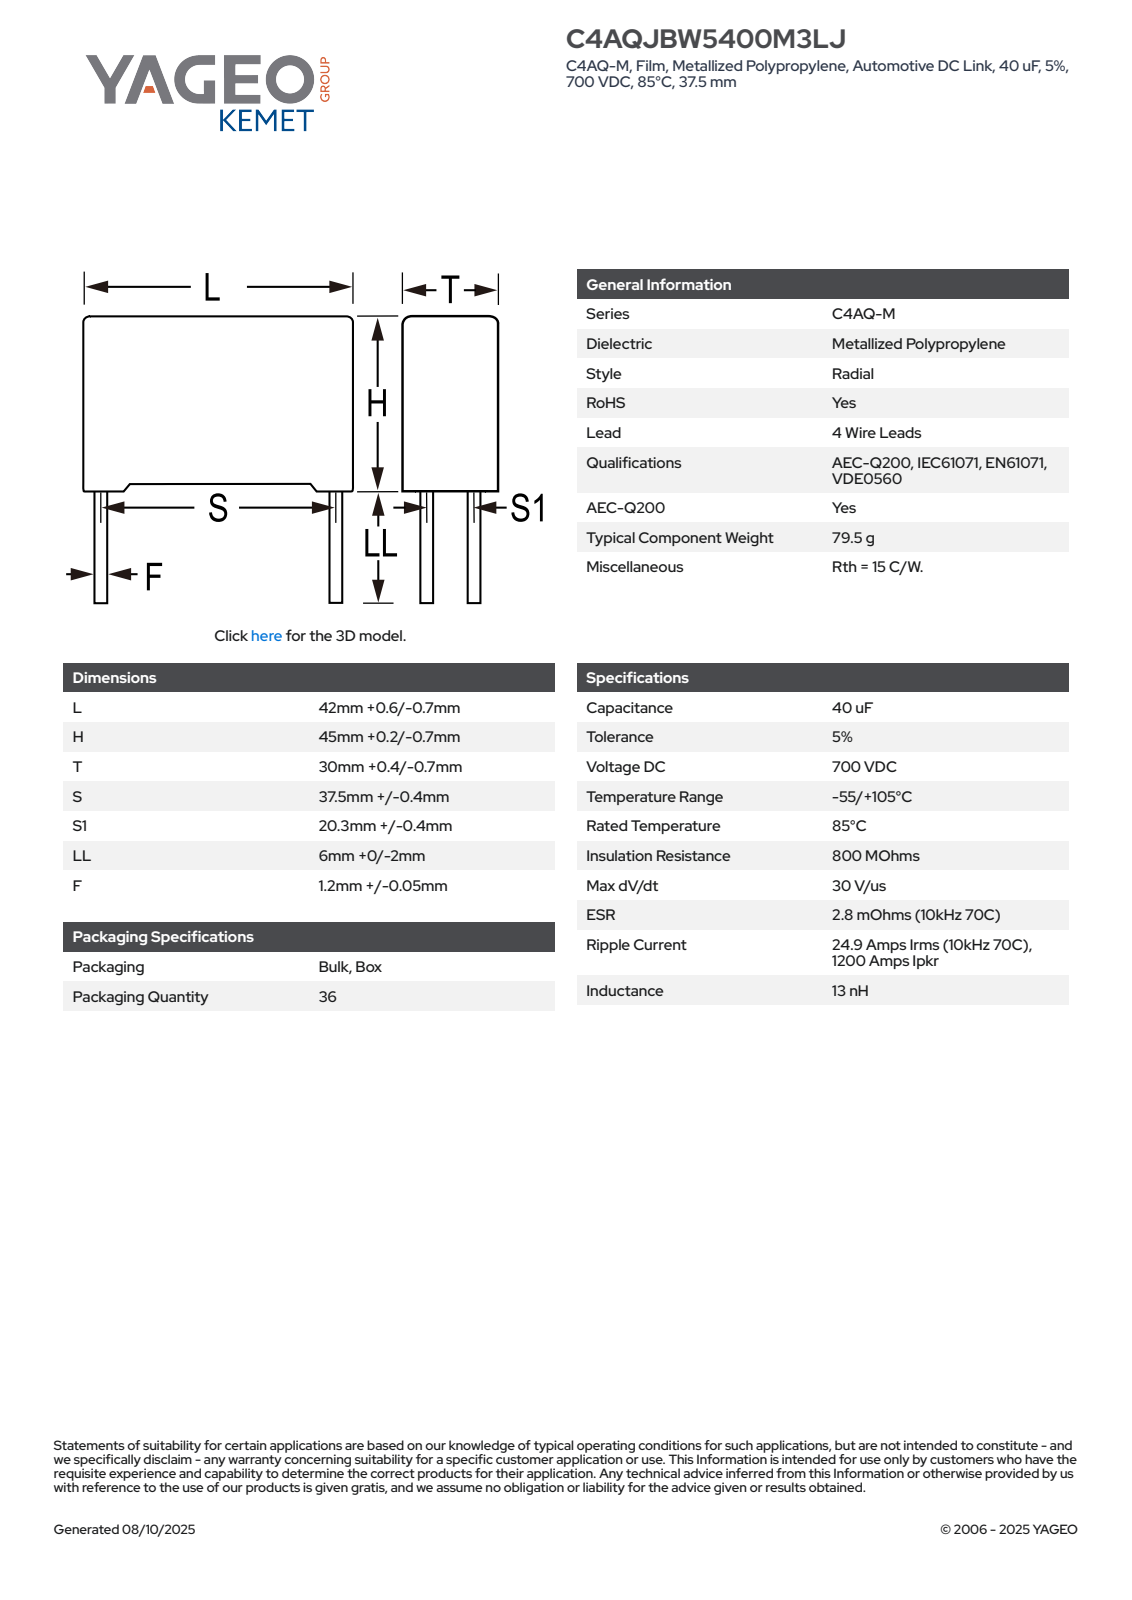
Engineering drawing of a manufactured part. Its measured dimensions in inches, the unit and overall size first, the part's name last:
Units: inches
Overall size (bounding box): 2.016 × 1.677 × 1.197
Round bosses / shafts (diameter × count): ⌀0.049 ×4
Main face-to-face distances: 1.197, 1.677, 1.727, 0.052, 1.78, 0.074, 1.604, 1.197, 1.53, 1.123
Volume: 3.482 in³ · Surface area: 14.65 in²
Bodies: 4 solids, 87 faces (79 planar, 8 cylindrical, 0 other)
Part name (STEP PRODUCT): CFP_RB4_42X45X30_L42.6H45.2T30.4S37.5S120.3LL6F1.25
STEP written by: SolidWorks 2014 (AUTOMOTIVE_DESIGN)
